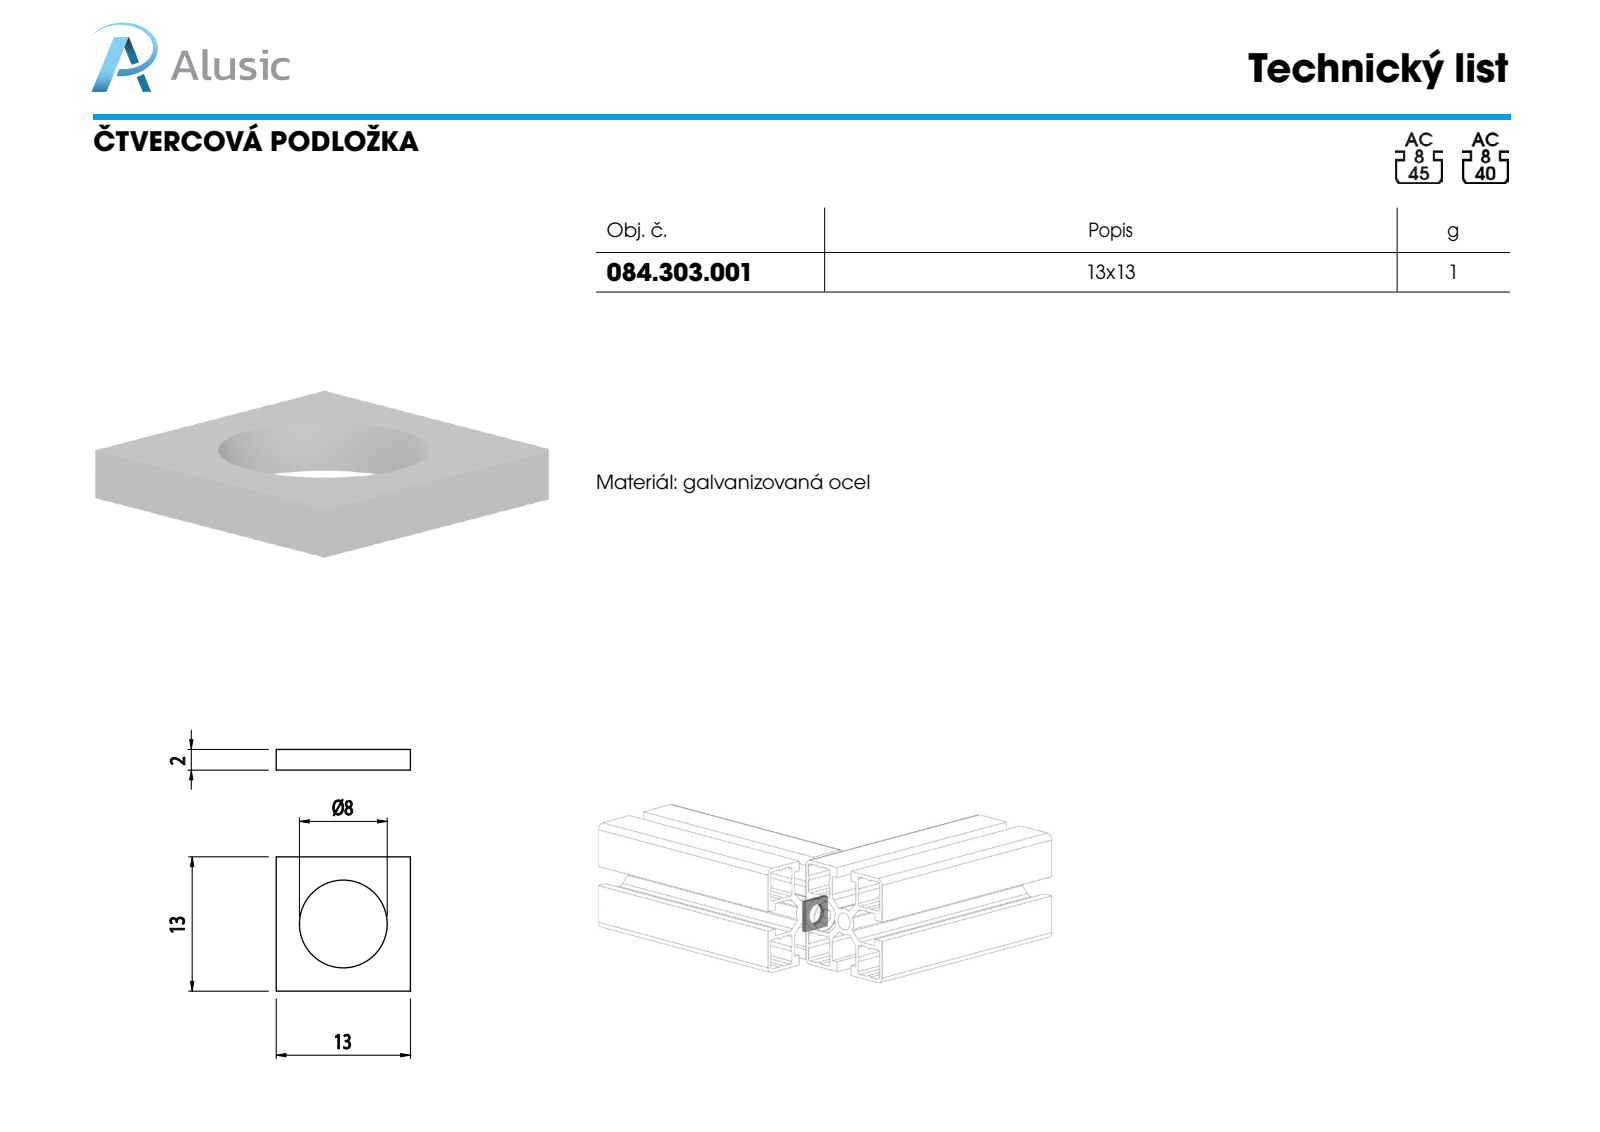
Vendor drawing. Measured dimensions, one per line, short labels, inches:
name: 084.303.001
written by: SolidWorks 2011 (CONFIG_CONTROL_DESIGN)
unit: in
bodies: 1 solid, 8 faces (6 planar, 2 cylindrical, 0 other)
size: 0.512 × 0.512 × 0.079
volume: 0.014 in³; area: 0.592 in²
holes: 1× ⌀0.335
face distances: 0.079, 0.512
